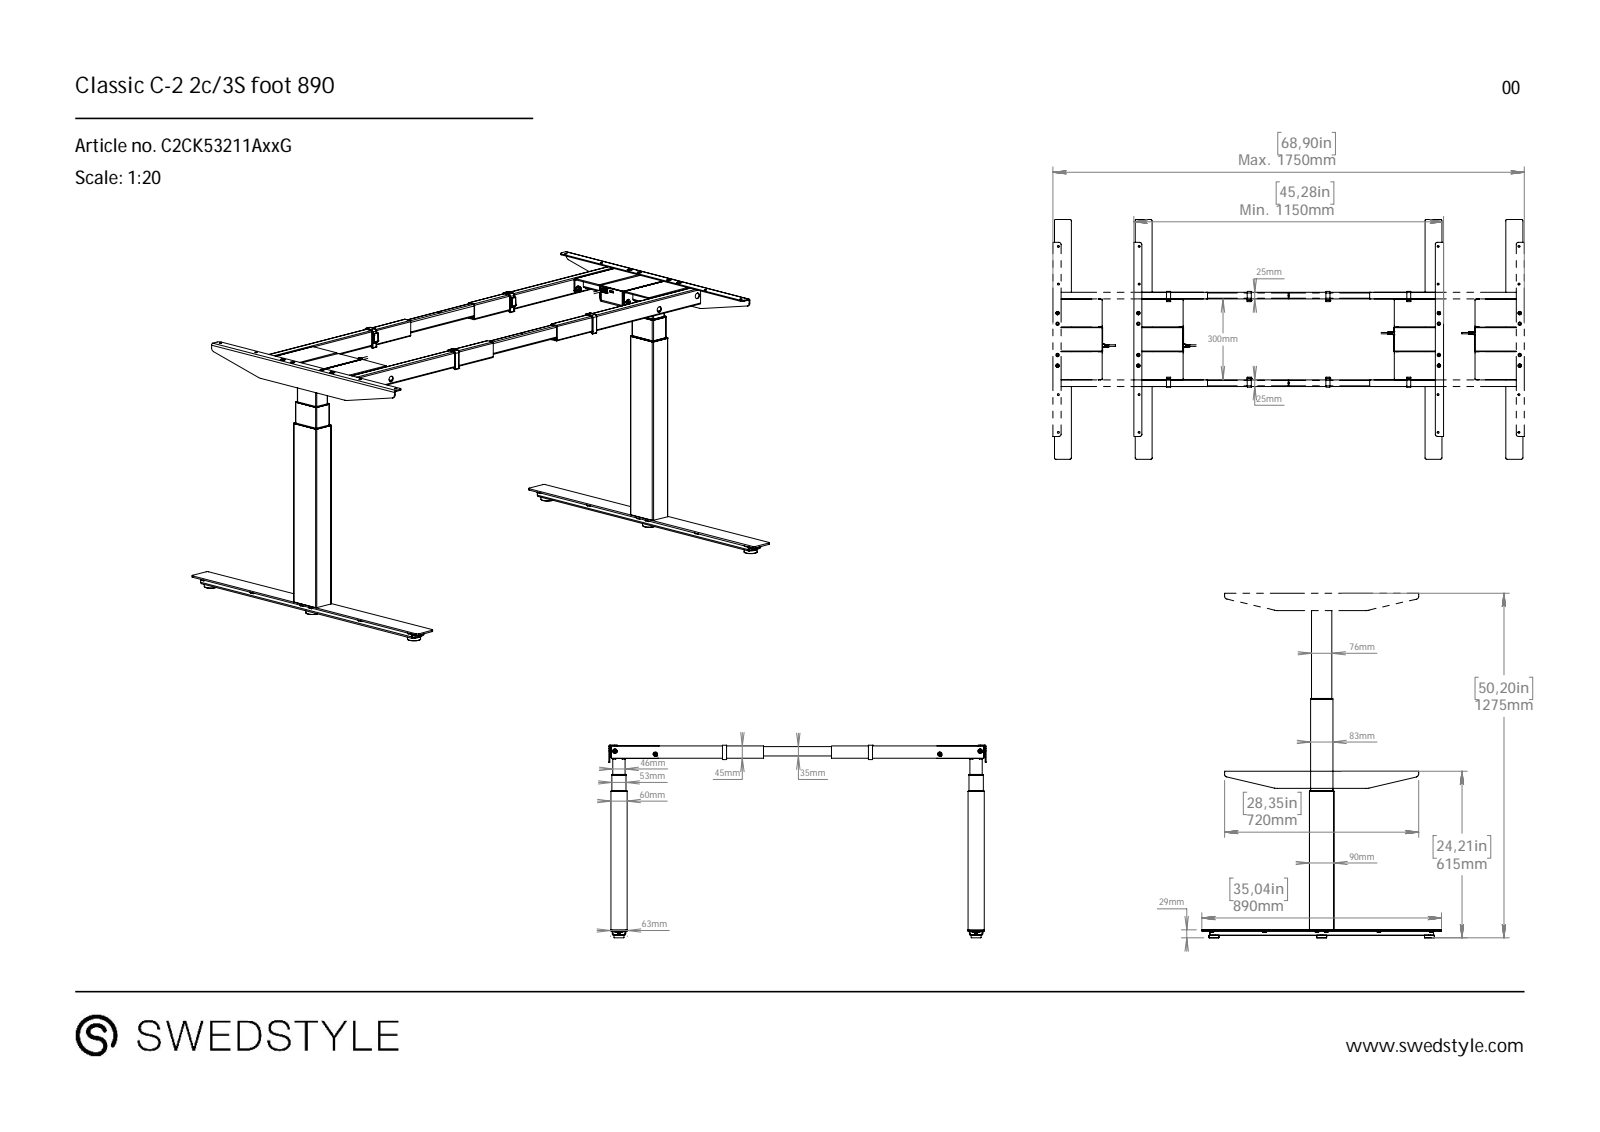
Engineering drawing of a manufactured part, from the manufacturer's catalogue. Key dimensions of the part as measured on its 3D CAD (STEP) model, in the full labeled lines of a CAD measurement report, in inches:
Part name (STEP PRODUCT): C2CK53211AxxG Classic C-2 2c_3S foot 890
STEP written by: SolidWorks 2021 (CONFIG_CONTROL_DESIGN)
Units: inches
Bodies: 0 solids, 1165 faces (527 planar, 348 cylindrical, 290 other)
Overall size (bounding box): 55.118 × 35.039 × 28.15
Round holes (diameter × count): ⌀0.63 ×12, ⌀0.276 ×8, ⌀0.295 ×4, ⌀0.315 ×4, ⌀0.213 ×2
Round bosses / shafts (diameter × count): ⌀0.613 ×2, ⌀0.335 ×2, ⌀0.315 ×2, ⌀0.217 ×2
Partial cylindrical surfaces — rounded edges, fillets, slot ends (radius × count): R0.098 ×64, R0.118 ×20, R0.02 ×18, R0.197 ×18, R0.11 ×16, R0.079 ×10, R0.138 ×8, R0.177 ×8
Main face-to-face distances: 0.138, 0.079, 0.276, 0.098, 52.205, 0.02, 2.087, 12.795, 0.118, 0.157
Hole centre spacings: 0.866, 1.33, 1.339, 1.594, 1.653, 2.024, 2.124, 2.974
